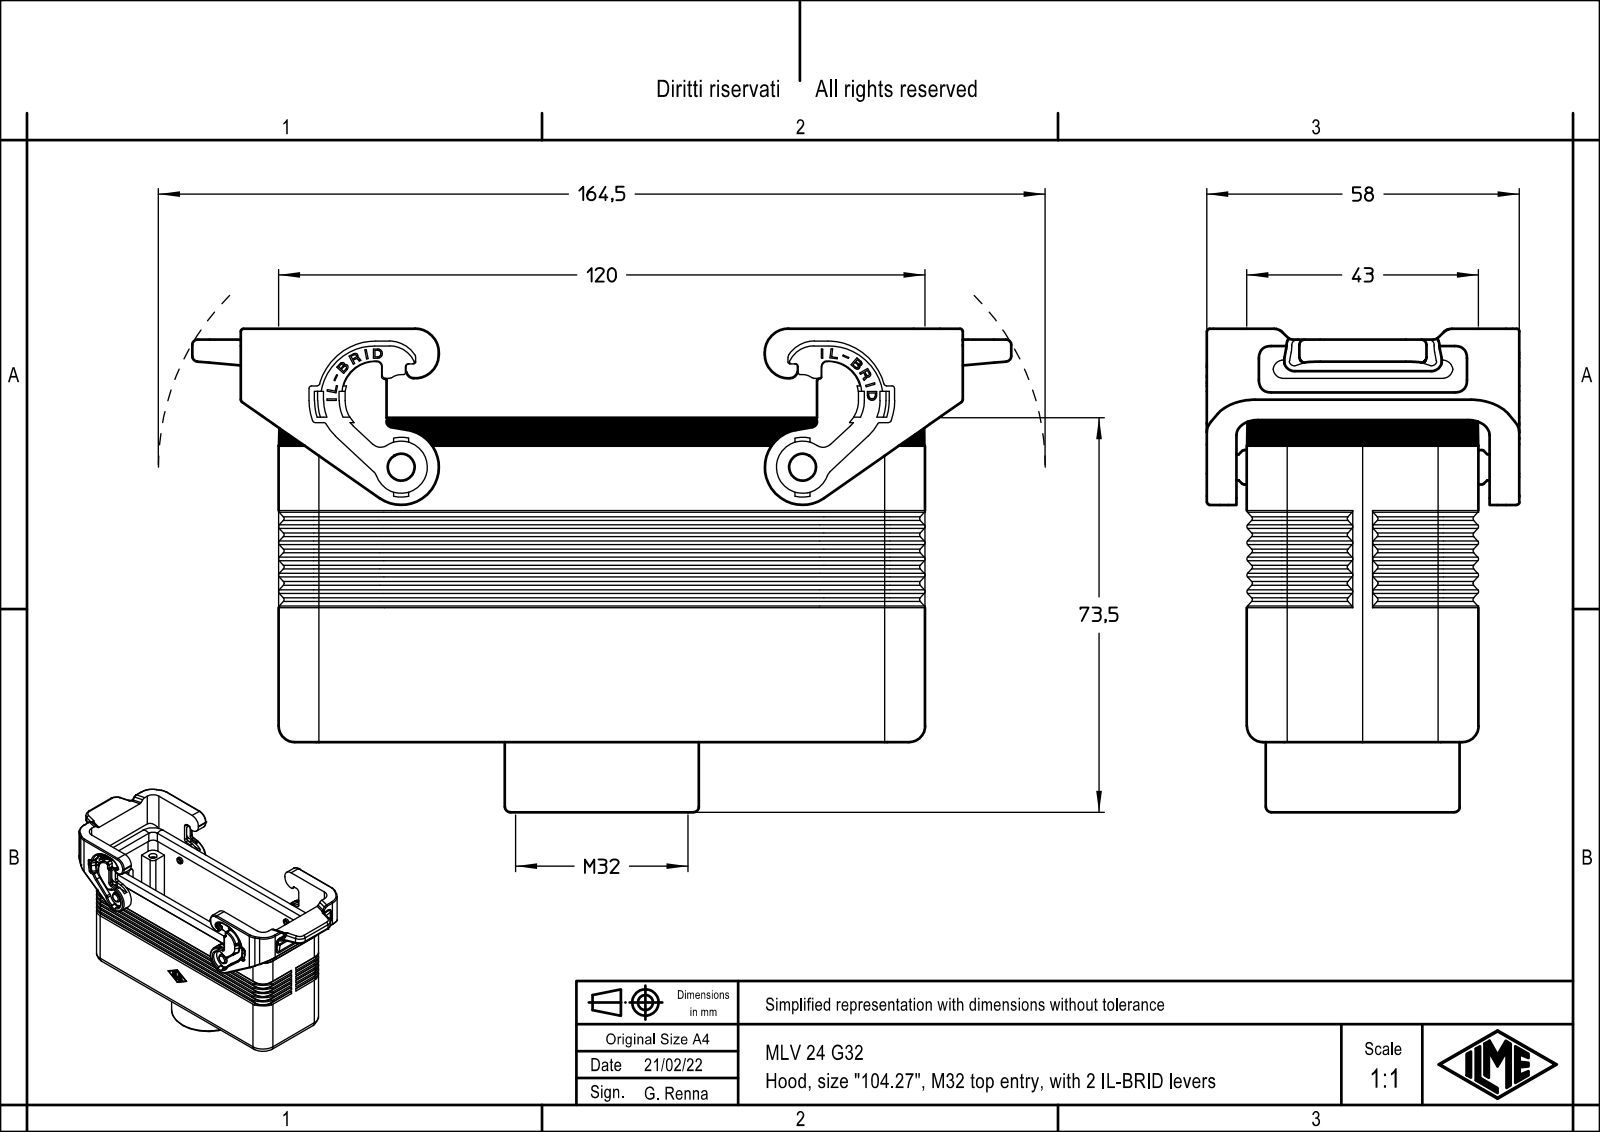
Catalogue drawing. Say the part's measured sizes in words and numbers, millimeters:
The part is named "MLV_24_G32". Its 3-D file was written by "Creo Elements/Direct Modeling 20.1B 02-Apr-2019 (C) Parametric Technology GmbH (AUTOMOTIVE_DESIGN)". It is 1 solid with 1544 faces: 967 planar, 385 cylindrical and 192 other. Overall it measures 152 by 89.7 by 58 millimeters. Its volume is 107 794 cubic millimeters and its surface area 63 793 square millimeters. Round holes: 4 of diameter 2.75, 1 of diameter 24, 1 of diameter 30.6. Round bosses or shafts: 2 of diameter 6.4, 2 of diameter 4.8, 1 of diameter 36. Partial cylindrical surfaces (rounded edges, fillets, slot ends): 74 of radius 0.5, 30 of radius 1, 26 of radius 1.5, 16 of radius 3, 15 of radius 0.33, 8 of radius 0.3, 8 of radius 2, 8 of radius 4. The main face-to-face distances are 3.5, 39.5, 2, 5.5, 36, 43, 47, 2.8, 3.4, 41.5. The hole center spacings are 53.72, 27, 104, 107.45.
